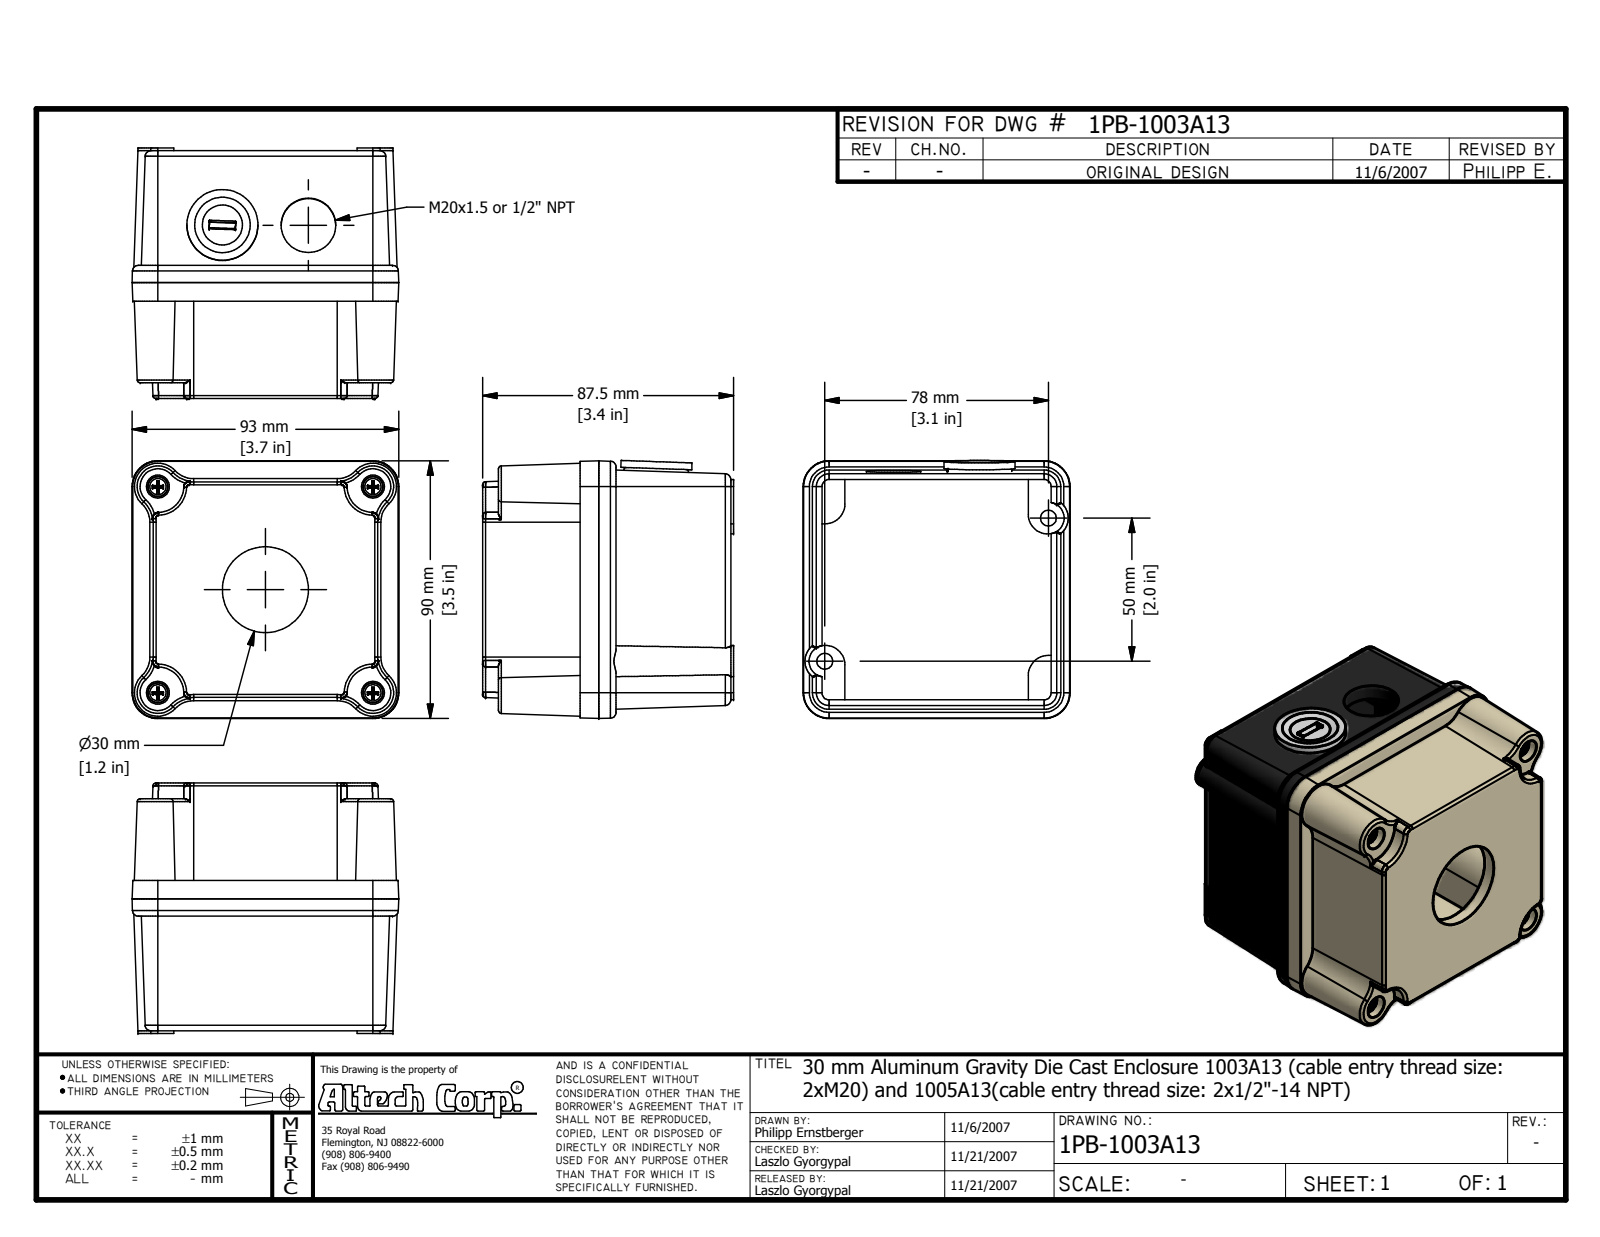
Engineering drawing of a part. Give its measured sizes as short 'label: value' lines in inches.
name: 209A13; enclosure_back; enclosure_front; ISO 7045 Z M4 x 5 - 4.8 - Z (+4 more)
written by: Autodesk Inventor 2008 (AUTOMOTIVE_DESIGN)
unit: in
bodies: 12 solids, 461 faces (168 planar, 66 cylindrical, 227 other)
size: 3.661 × 3.548 × 3.445
volume: 15.11 in³; area: 141 in²
holes: 4× ⌀0.138, 2× ⌀0.169, 2× ⌀0.748, 1× ⌀0.866
bosses: 4× ⌀0.125, 2× ⌀0.354, 2× ⌀0.157, 2× ⌀0.143, 1× ⌀0.974
rounds: 8× R0.079, 4× R0.039, 4× R0.097, 4× R0.354, 2× R0.217, 2× R0.236, 2× R0.268, 2× R0.276
face distances: 1.811, 1.594, 3.406, 0.236, 1.575, 3.228, 3.169, 0.177, 1.417, 2.992
hole spacings: 2.046, 1.201, 1.319, 1.656, 2.835, 2.953, 3.019, 3.227
